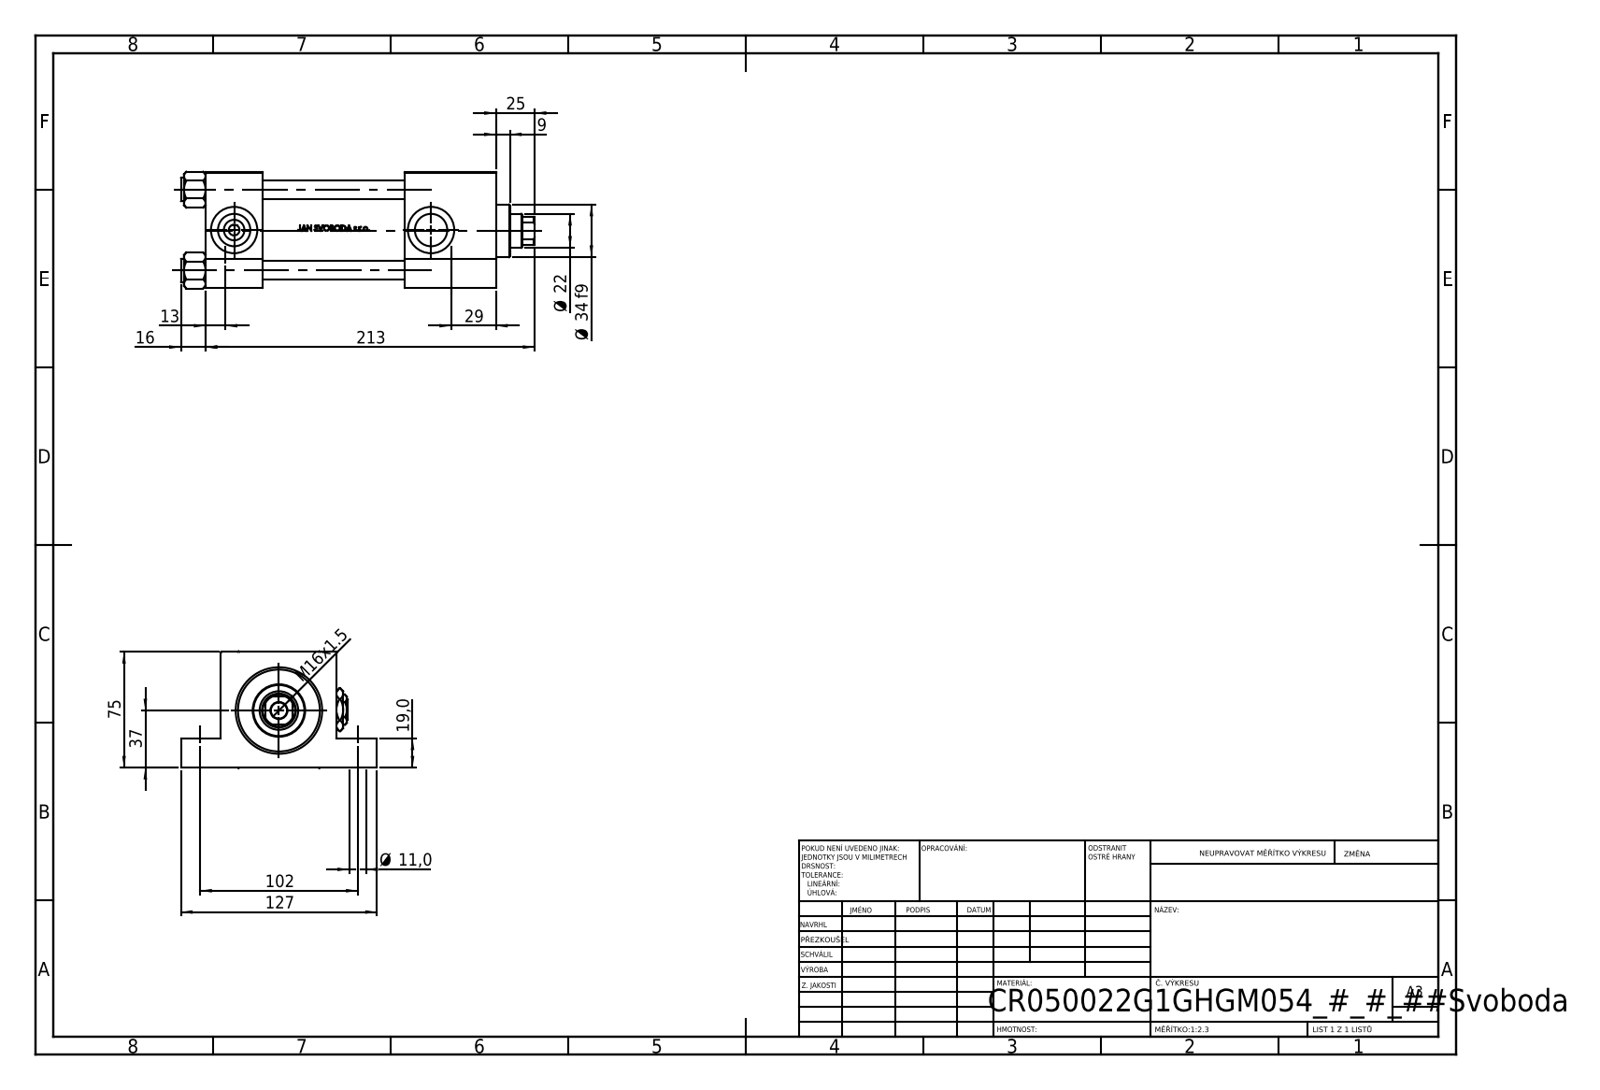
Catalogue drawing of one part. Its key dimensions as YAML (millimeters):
part_name: "Zatka_pro_OIL_PORT; V215CR_G_TYCINKA; V215CR_G_Body; NUT_M5_G (+2 more)"
step_written_by: "SolidWorks 2019 (CONFIG_CONTROL_DESIGN)"
units: millimeters
bodies: {solids: 12, faces: 1134, planar: 454, cylindrical: 128, other: 552}
overall_size: [229, 127, 75.54]
volume: 797692
surface_area: 180103
round_holes:
  - {diameter: 11, count: 4}
  - {diameter: 12, count: 4}
  - {diameter: 7, count: 2}
  - {diameter: 20.96, count: 2}
  - {diameter: 30, count: 2}
  - {diameter: 10.5, count: 1}
  - {diameter: 22, count: 1}
  - {diameter: 25, count: 1}
  - {diameter: 41, count: 1}
  - {diameter: 50, count: 1}
  - {diameter: 53, count: 1}
round_bosses_or_shafts:
  - {diameter: 15, count: 4}
  - {diameter: 56, count: 1}
  - {diameter: 34, count: 1}
partial_cylinders:
  - {radius: 10.5, count: 1}
face_to_face_distances: [75, 37, 188, 151, 19, 56, 59, 129, 92, 26]
hole_center_spacings: [52.3, 36.63, 37.34, 73.96, 102, 146, 178.1, 127.5]
